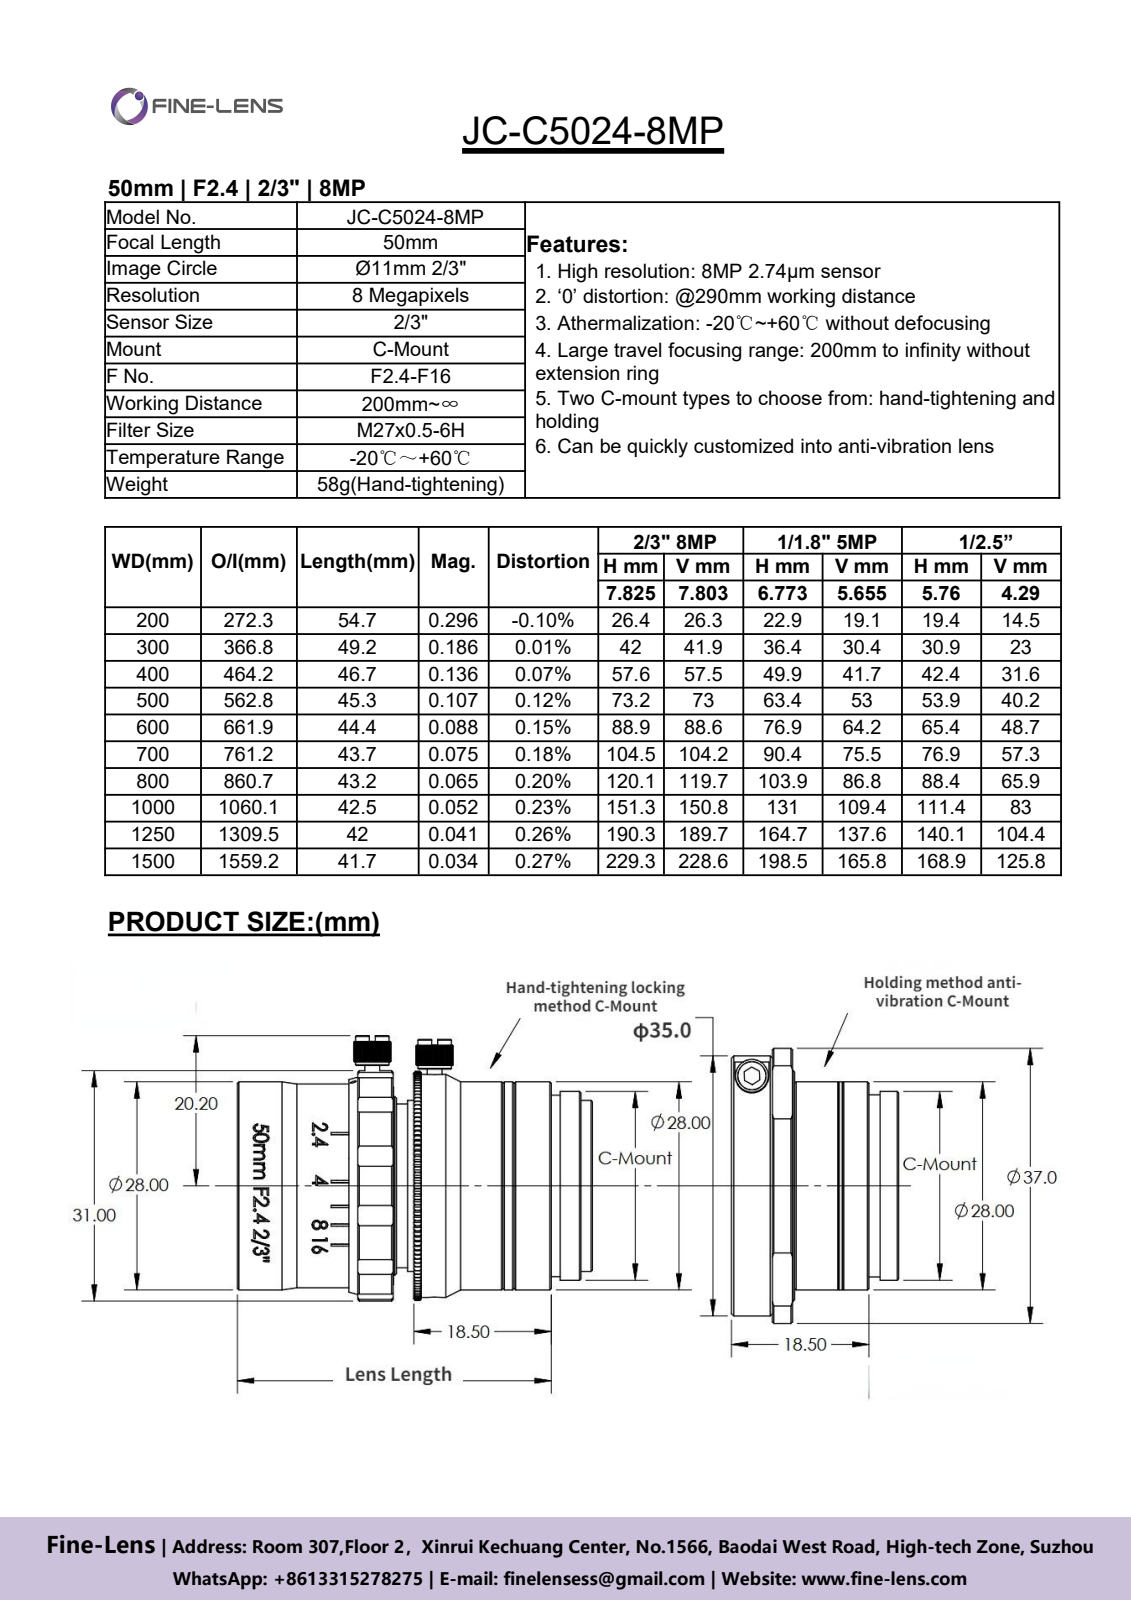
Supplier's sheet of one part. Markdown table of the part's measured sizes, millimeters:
| quantity | value |
| --- | --- |
| STEP written by | SolidWorks 2016 (CONFIG_CONTROL_DESIGN) |
| units | millimeters |
| bodies | 3 solids, 1125 faces (425 planar, 245 cylindrical, 455 other) |
| overall size | 49.38 × 31 × 31 |
| volume | 17 348 mm³ |
| surface area | 14 263 mm² |
| round holes (diameter × count) | 1.6 × 2, 0.8 × 1, 17.8 × 1, 20.5 × 1, 22.4 × 1, 24.6 × 1, 25.2 × 1, 26.5 × 1, 27.2 × 1, 27.6 × 1, 29 × 1 |
| round bosses / shafts (diameter × count) | 30 × 1, 28 × 1, 27.4 × 1, 25.4 × 1, 24.4 × 1, 24 × 1, 23.2 × 1, 23 × 1 |
| partial cylindrical surfaces (radius × count) | 2.5 × 12, 1 × 1, 13.75 × 1, 14.05 × 1, 15.4 × 1, 15.5 × 1 |
| main face-to-face distances | 4, 45, 41, 24.08, 20.08, 20.92, 36.08, 32.08, 12, 8.92 |
